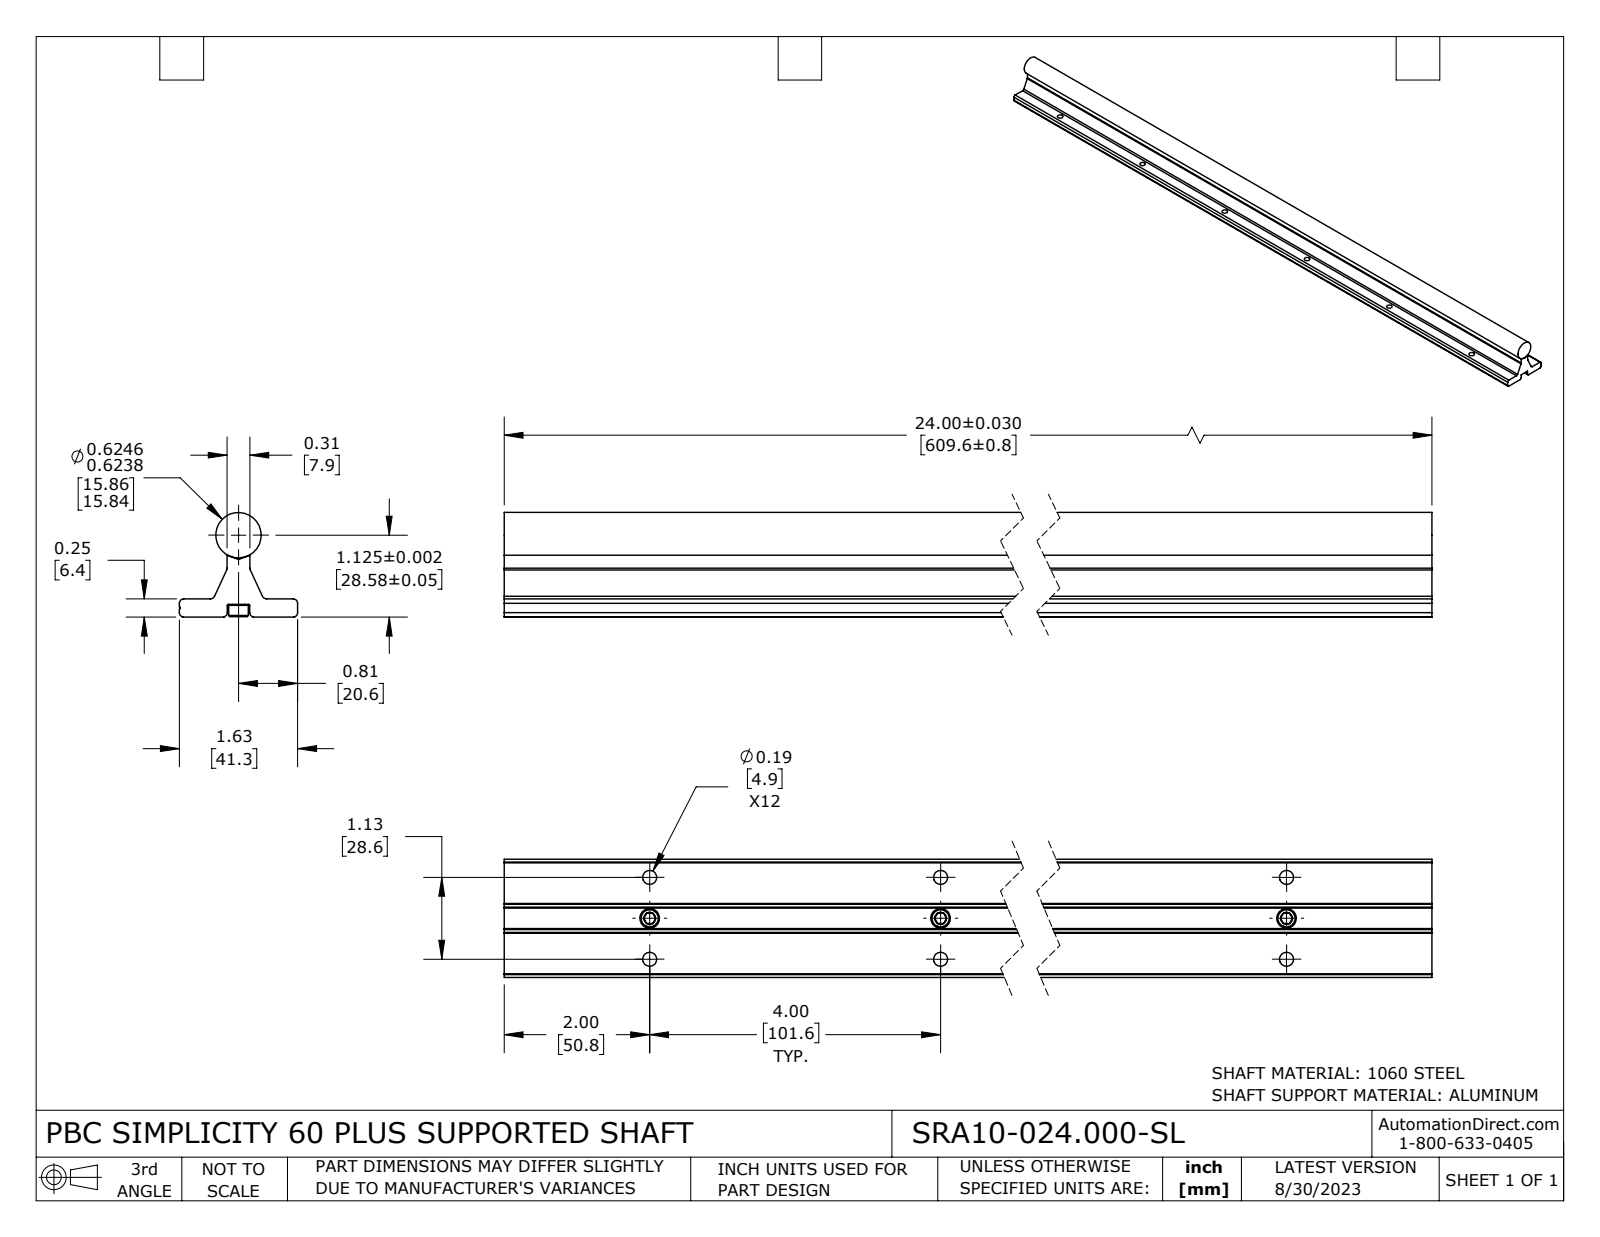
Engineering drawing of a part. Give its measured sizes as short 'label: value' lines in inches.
name: SRA10-024.000-SL
written by: SolidWorks 2021 (CONFIG_CONTROL_DESIGN)
unit: in
bodies: 8 solids, 281 faces (93 planar, 98 cylindrical, 90 other)
size: 24 × 1.625 × 1.438
volume: 21.78 in³; area: 174.1 in²
holes: 18× ⌀0.194, 6× ⌀0.141, 6× ⌀0.188
bosses: 6× ⌀0.27, 6× ⌀0.165, 1× ⌀0.625
rounds: 6× R0.06, 2× R0.015, 2× R0.062, 2× R0.063
face distances: 0.25, 0.174, 0.076, 0.656, 0.969, 0.657, 0.968, 0.311, 0.313, 1.625
hole spacings: 4.039, 8.02, 4, 0.563, 8, 12.013, 4.155, 12
